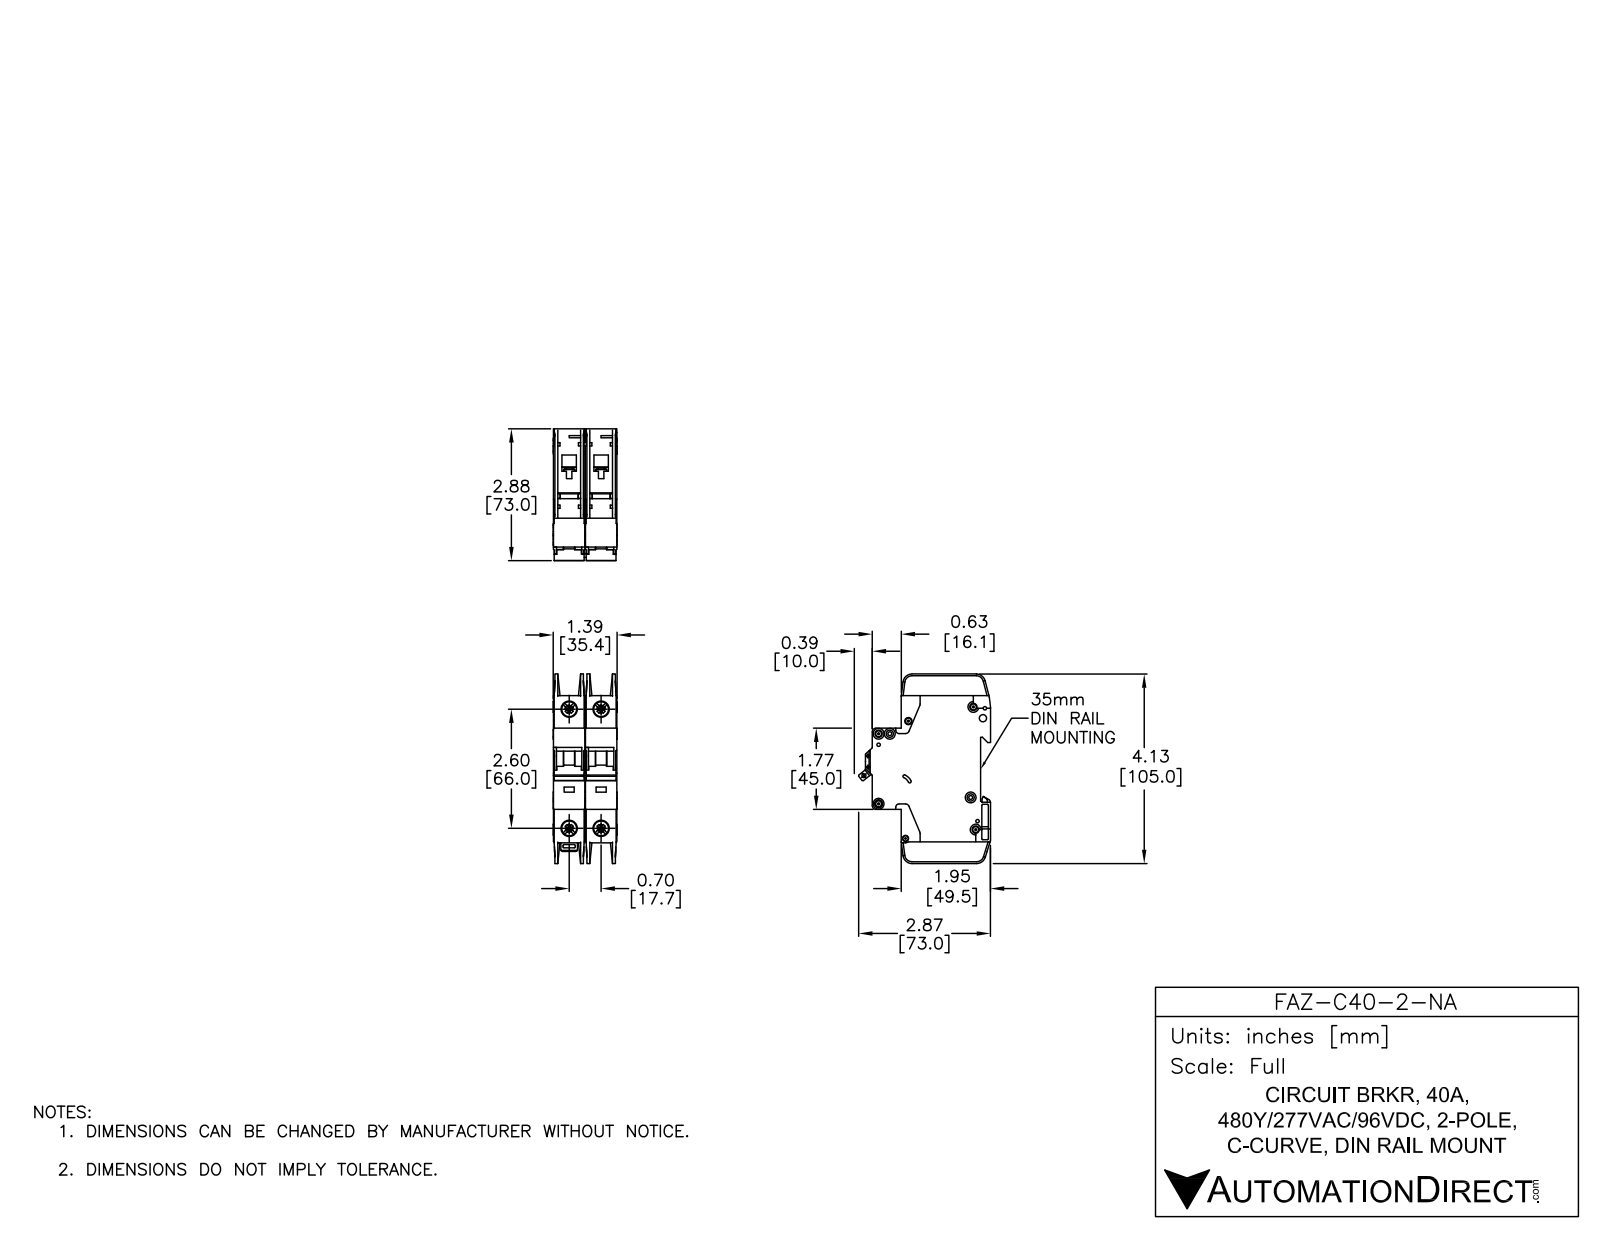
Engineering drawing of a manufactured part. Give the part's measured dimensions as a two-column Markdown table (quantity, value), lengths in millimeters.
| quantity | value |
| --- | --- |
| part name | FAZ-C40-2-NA |
| STEP written by | SolidWorks 2014 (AUTOMOTIVE_DESIGN) |
| units | millimeters |
| bodies | 6 solids, 1568 faces (818 planar, 526 cylindrical, 224 other) |
| overall size | 105 × 73.04 × 35.4 |
| volume | 155 390 mm³ |
| surface area | 49 479 mm² |
| round holes (diameter × count) | 3.6 × 7, 7.15 × 4, 8.2 × 4, 1.09 × 2, 1.5 × 2, 4 × 2, 1.9 × 1, 2.15 × 1, 2.2 × 1, 2.55 × 1, 3.3 × 1, 3.4 × 1 |
| round bosses / shafts (diameter × count) | 6 × 7, 2.5 × 2 |
| partial cylindrical surfaces (radius × count) | 0.25 × 47, 0.5 × 24, 1 × 18, 2 × 12, 5 × 5, 1.8 × 4, 4 × 4, 0.2 × 2 |
| main face-to-face distances | 17.7, 17.5, 0.7, 15.05, 2.45, 1.75, 15.75, 13.3, 35.2, 17 |
| hole center spacings | 6.2, 17.7, 66, 68.33, 5.19, 6.1, 8.19, 8.56 |
